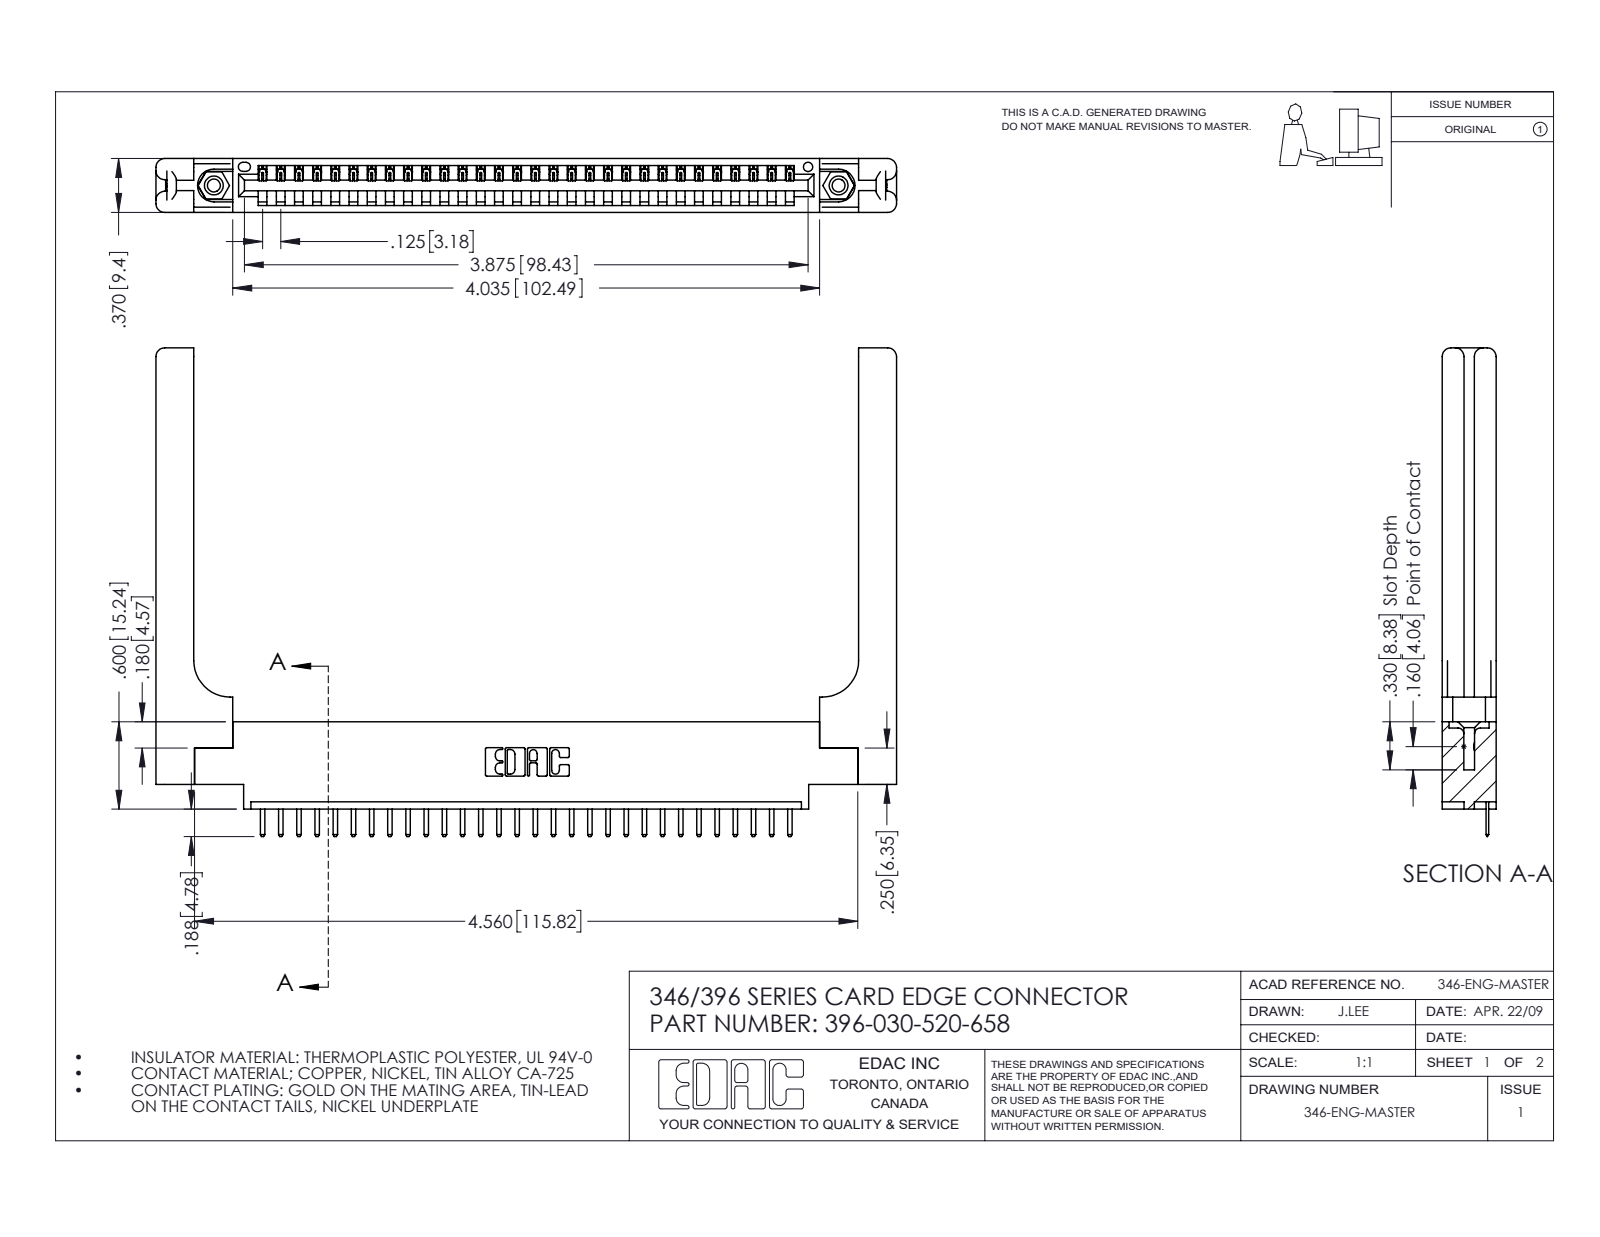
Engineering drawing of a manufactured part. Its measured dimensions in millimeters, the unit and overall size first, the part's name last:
Units: millimetres
Overall size (bounding box): 129.3 × 85.3 × 9.4
Round holes (diameter × count): ⌀2.3 ×2, ⌀3.2 ×2, ⌀4 ×2, ⌀1.6 ×1
Round bosses / shafts (diameter × count): ⌀3.9 ×2
Partial cylindrical surfaces — rounded edges, fillets, slot ends (radius × count): R0.3 ×62, R0.2 ×60, R0.3 ×22, R1.5 ×16, R0.2 ×6, R0.8 ×6, R0.7 ×3, R0.8 ×2
Main face-to-face distances: 9.4, 1.8, 1.2, 8.2, 3.8, 3.8, 6.4, 7.6, 0.6, 1.9
Hole centre spacings: 6.2, 103.8, 109.1
Volume: 19 570 mm³ · Surface area: 19 980 mm²
Bodies: 35 solids, 2242 faces (1488 planar, 694 cylindrical, 60 other)
Part name (STEP PRODUCT): 346 Part_0.170 Offset - 0.156 Dia-TH; 346-220-058_345-220-058; 396-030-520-658; 345-292-001_345-293-120 (+1 more)
STEP written by: SolidWorks 2016 (CONFIG_CONTROL_DESIGN)
